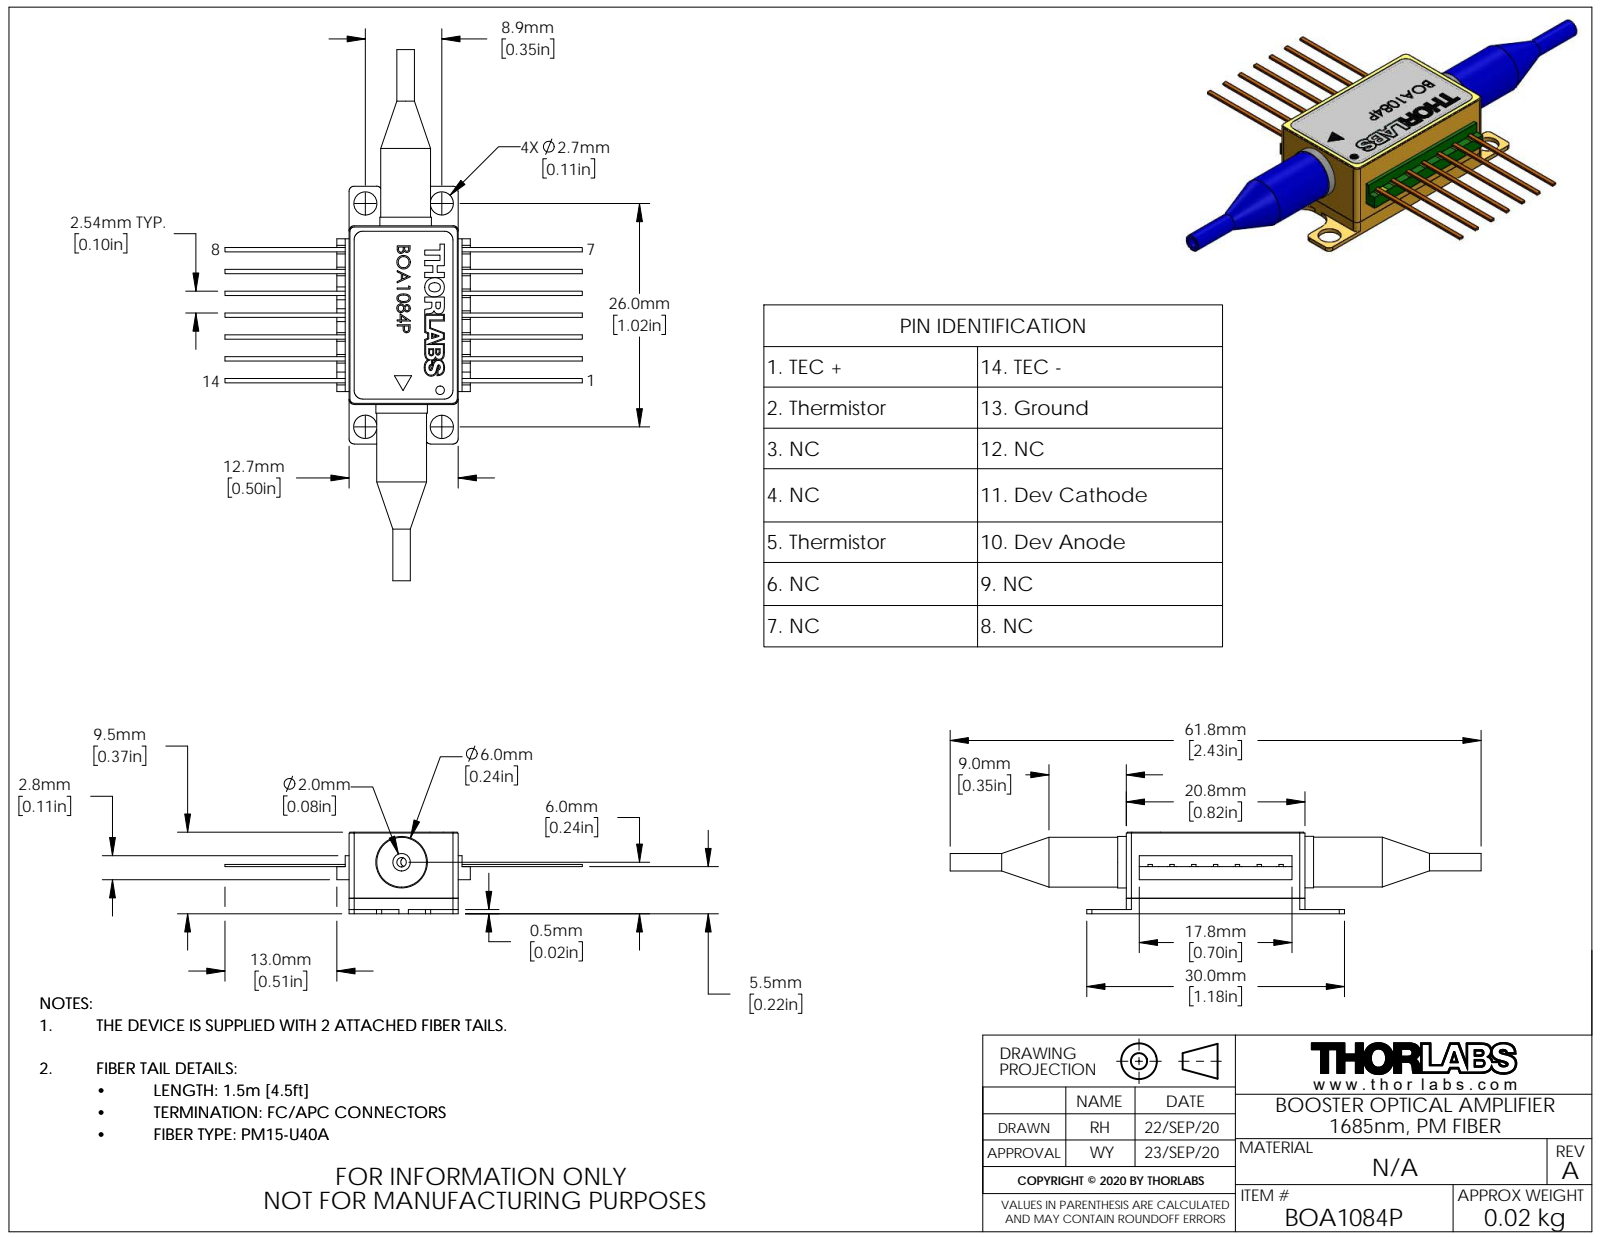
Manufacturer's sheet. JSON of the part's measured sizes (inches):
{"part_name": "QTN040800-E0W", "step_written_by": "SolidWorks 2018 (AUTOMOTIVE_DESIGN)", "units": "inches", "bodies": {"solids": 0, "faces": 397, "planar": 275, "cylindrical": 50, "other": 72}, "overall_size": [2.433, 1.638, 0.374], "round_holes": [[0.106, 4], [0.043, 2], [0.039, 1]], "round_bosses_or_shafts": [[0.236, 2], [0.228, 2], [0.08, 2]], "partial_cylinders_radius": [[0.024, 12], [0.02, 4], [0.079, 4]], "face_to_face_distances": [0.374, 0.5, 0.071, 0.303, 0.06, 0.216, 0.145, 0.158, 0.085, 0.156], "hole_center_spacings": [0.35, 1.024, 1.082, 0.019, 0.168, 0.381, 0.856, 0.922]}
